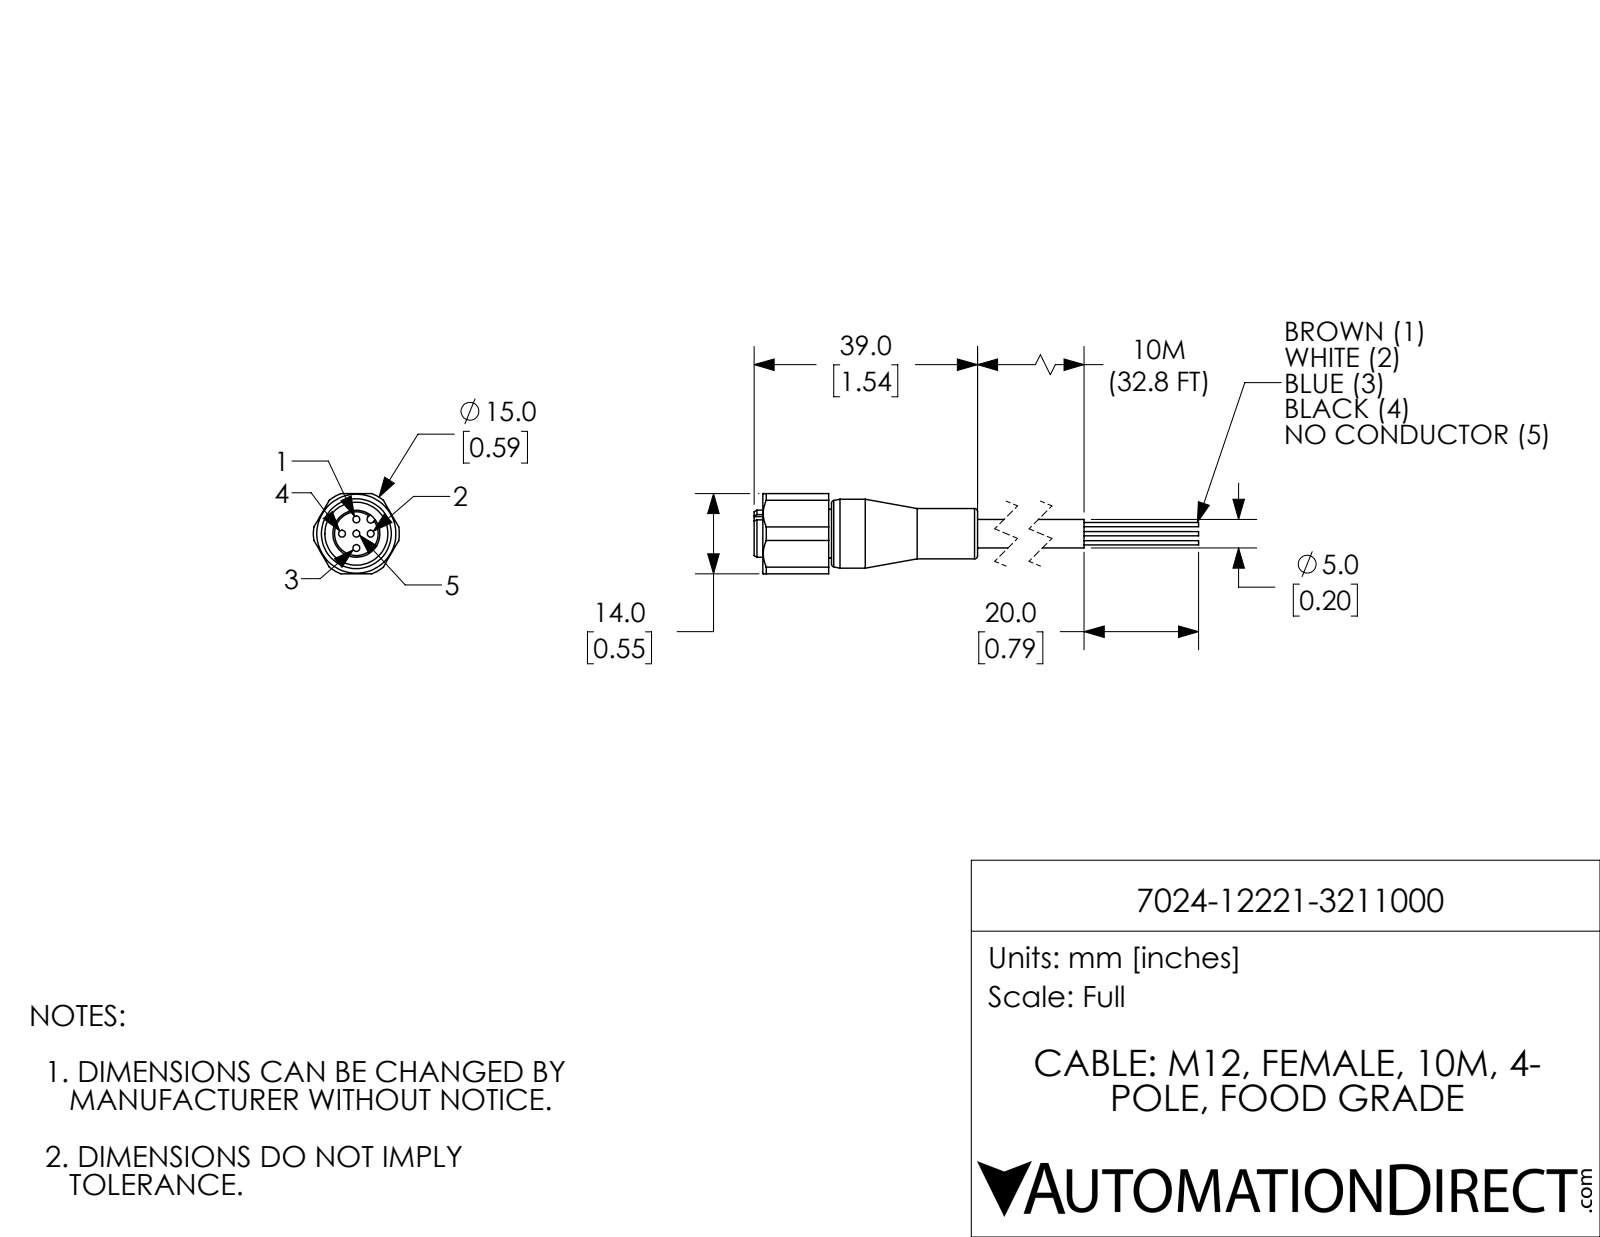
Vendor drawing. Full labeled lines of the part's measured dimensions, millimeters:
Part name (STEP PRODUCT): 7024-12221-3211000
STEP written by: SolidWorks 2018 (AUTOMOTIVE_DESIGN)
Units: millimetres
Bodies: 1 solid, 77 faces (25 planar, 37 cylindrical, 15 other)
Overall size (bounding box): 77.8 × 15 × 14
Volume: 4 116 mm³ · Surface area: 2 828 mm²
Round holes (diameter × count): ⌀1.2 ×5, ⌀11 ×1
Round bosses / shafts (diameter × count): ⌀0.76 ×4, ⌀12 ×1, ⌀8.8 ×1, ⌀8.5 ×1, ⌀8.2 ×1, ⌀5 ×1
Partial cylindrical surfaces — rounded edges, fillets, slot ends (radius × count): R0.65 ×1, R7.5 ×1
Main face-to-face distances: 14, 4, 9, 13, 1.5, 7.5, 11.5, 13.5, 12, 4.5
Hole centre spacings: 2.5, 3.54, 5
